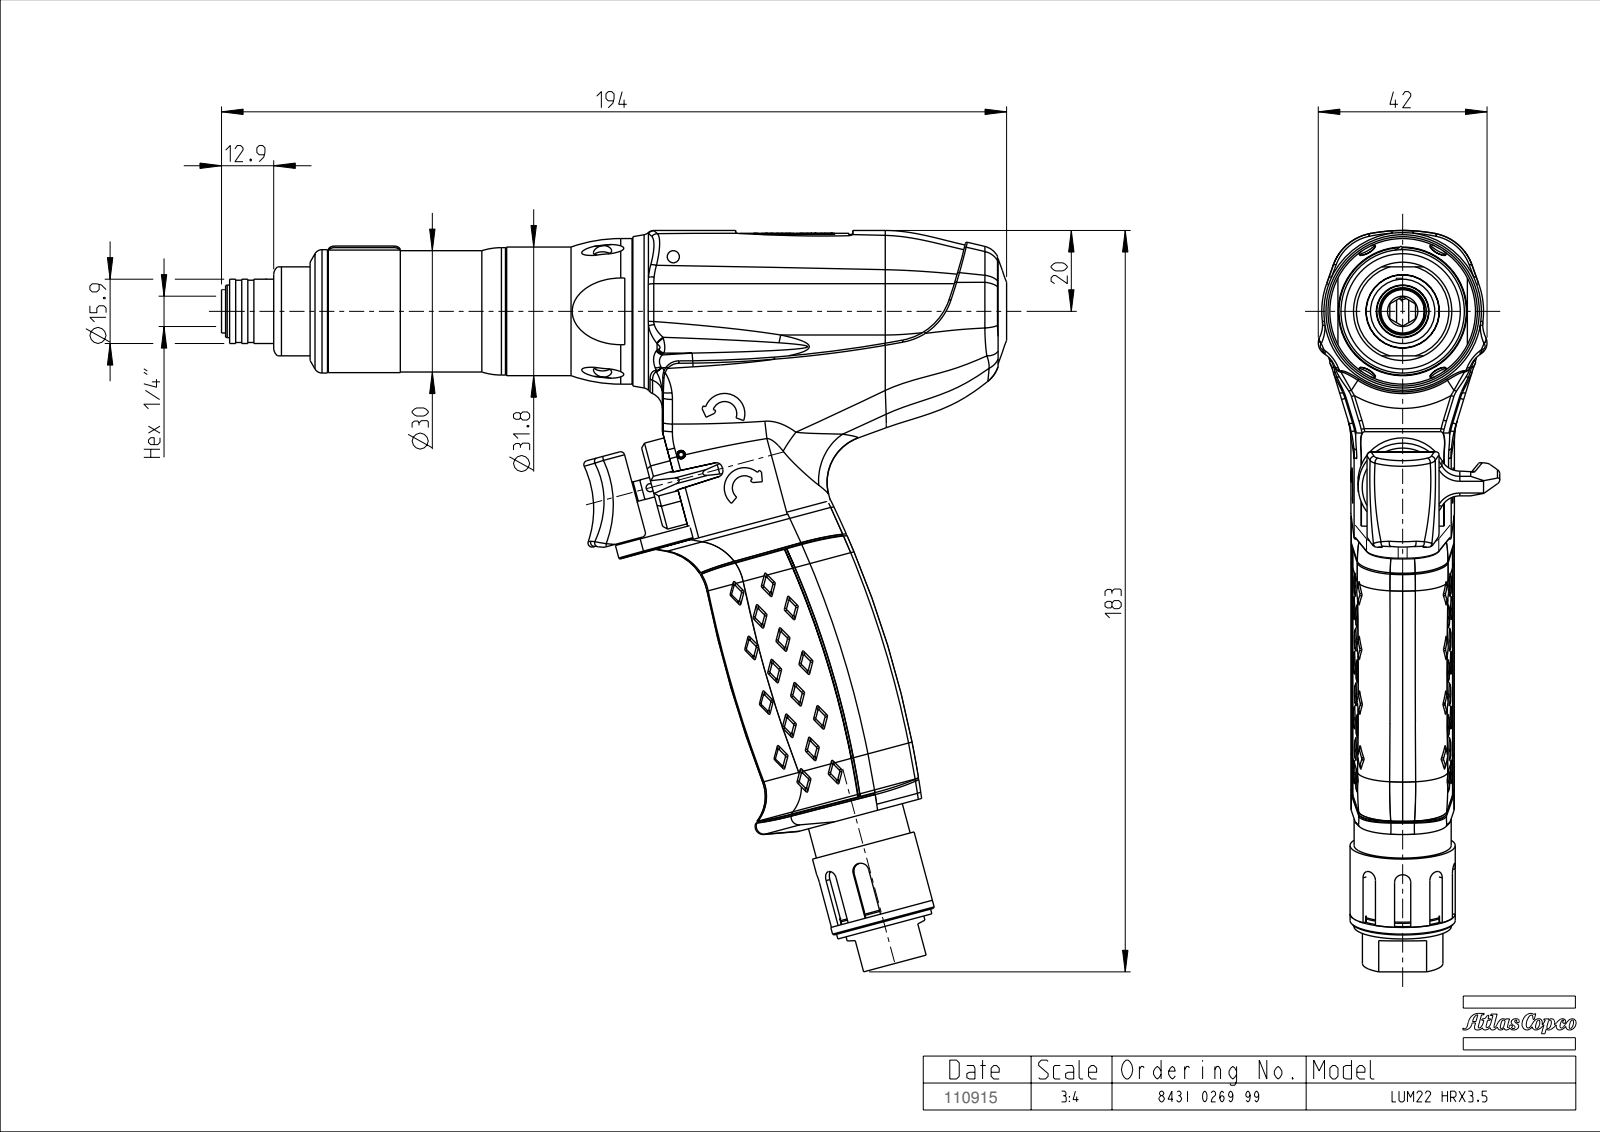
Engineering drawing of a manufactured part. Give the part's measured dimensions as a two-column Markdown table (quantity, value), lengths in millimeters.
| quantity | value |
| --- | --- |
| part name | TMP142648_SW |
| STEP written by | PRO/ENGINEER BY PARAMETRIC TECHNOLOGY CORPORATION, 2008310 (CONFIG_CONTROL_DESIGN) |
| units | millimeters |
| bodies | 0 solids, 818 faces (158 planar, 163 cylindrical, 497 other) |
| overall size | 194.1 × 183.3 × 44.87 |
| round holes (diameter × count) | 4.5 × 2, 3 × 1, 7.5 × 1, 11.45 × 1 |
| round bosses / shafts (diameter × count) | 36 × 1, 31.8 × 1, 31.5 × 1, 30.5 × 1, 30.3 × 1, 30 × 1, 26 × 1, 24.1 × 1 |
| partial cylindrical surfaces (radius × count) | 1 × 16, 2.5 × 5, 0.5 × 4, 1.5 × 4, 2 × 4, 3.3 × 4, 4 × 3, 5 × 3 |
| main face-to-face distances | 0.8, 6.34, 1.5, 80, 6, 12.83, 19.17, 5.99, 19.5, 27.01 |
